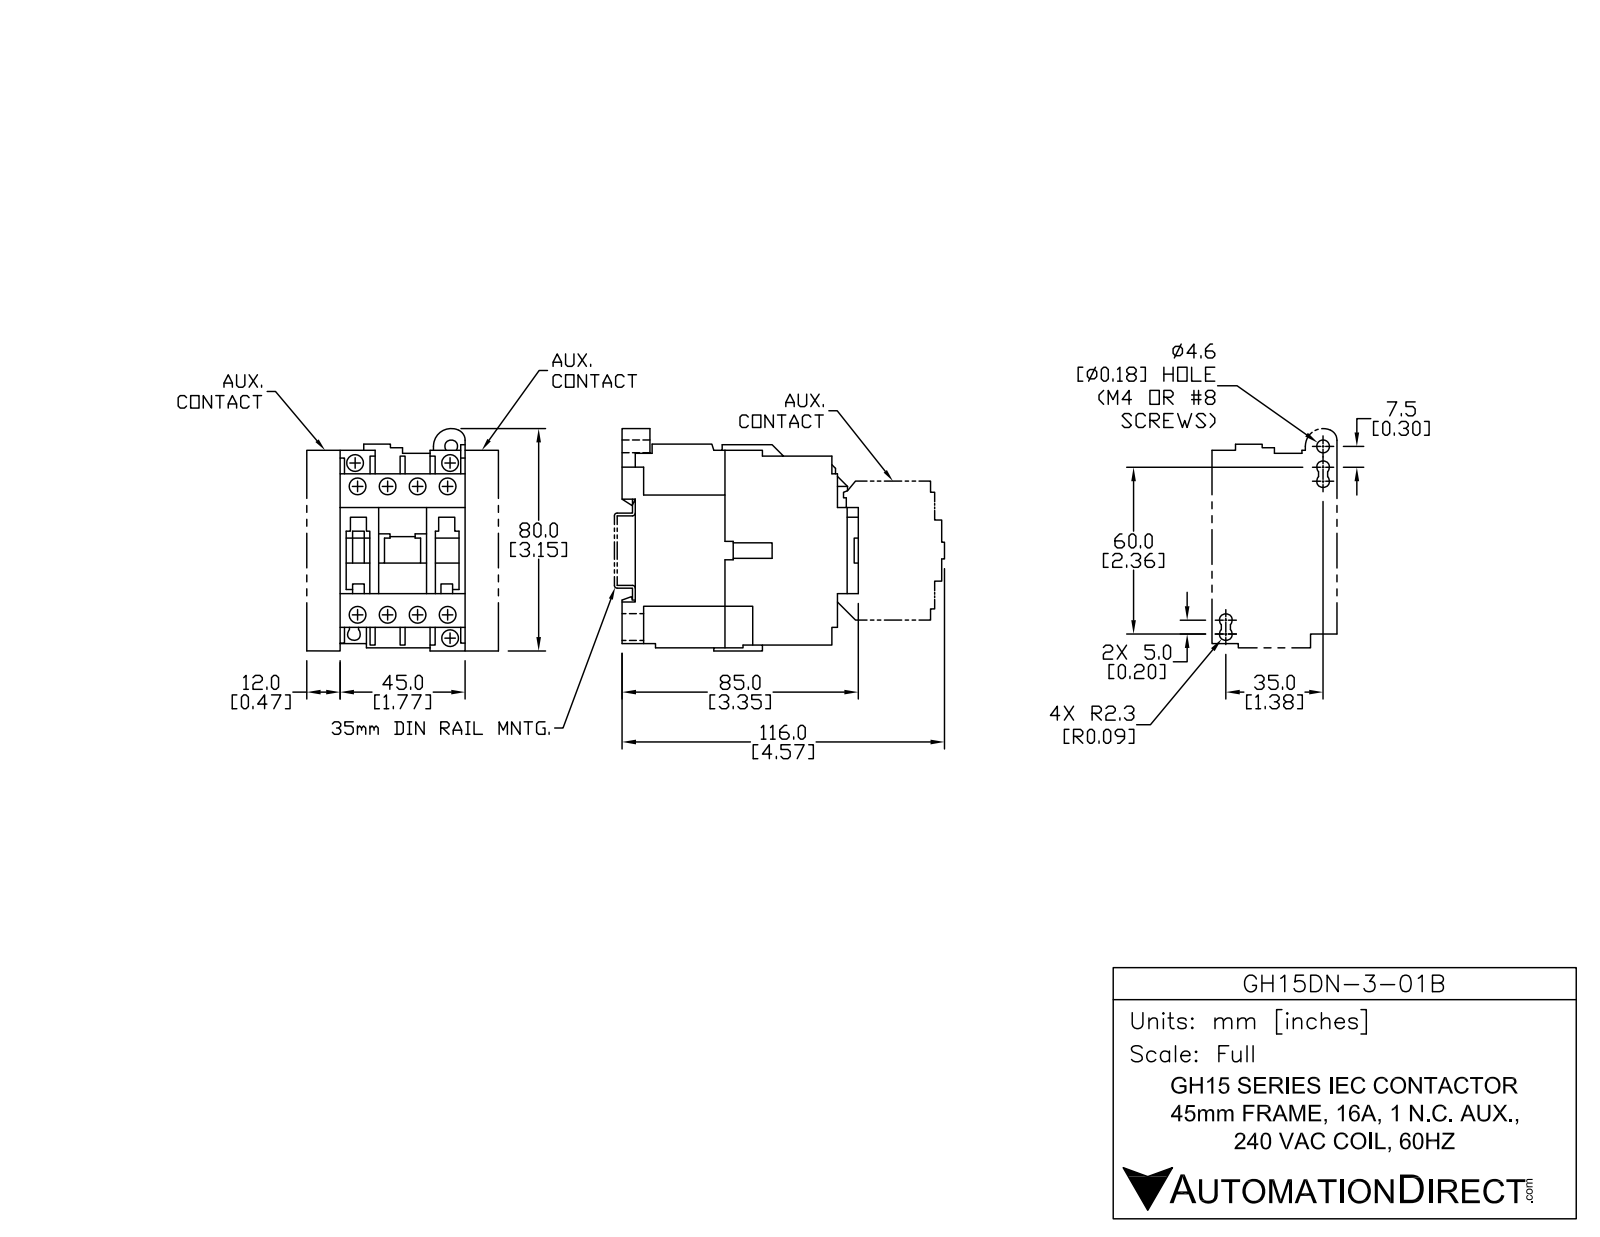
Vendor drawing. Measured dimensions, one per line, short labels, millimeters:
name: GH15DN-3-01B
written by: SolidWorks 2009 (AUTOMOTIVE_DESIGN)
unit: mm
bodies: 1 solid, 666 faces (447 planar, 65 cylindrical, 154 other)
size: 85.5 × 80 × 45
volume: 196 351 mm³; area: 35 792 mm²
holes: 9× ⌀6.25, 2× ⌀6.5, 1× ⌀4.6
rounds: 10× R1, 8× R2.3, 8× R4.75, 2× R3, 1× R4.99, 1× R5
face distances: 45, 9.5, 35.5, 12.12, 23.38, 8, 7, 33.75, 10.38, 32.87
hole spacings: 11.25, 47.12, 22.5, 45.76, 50.99, 7.62, 33.75, 53.38
